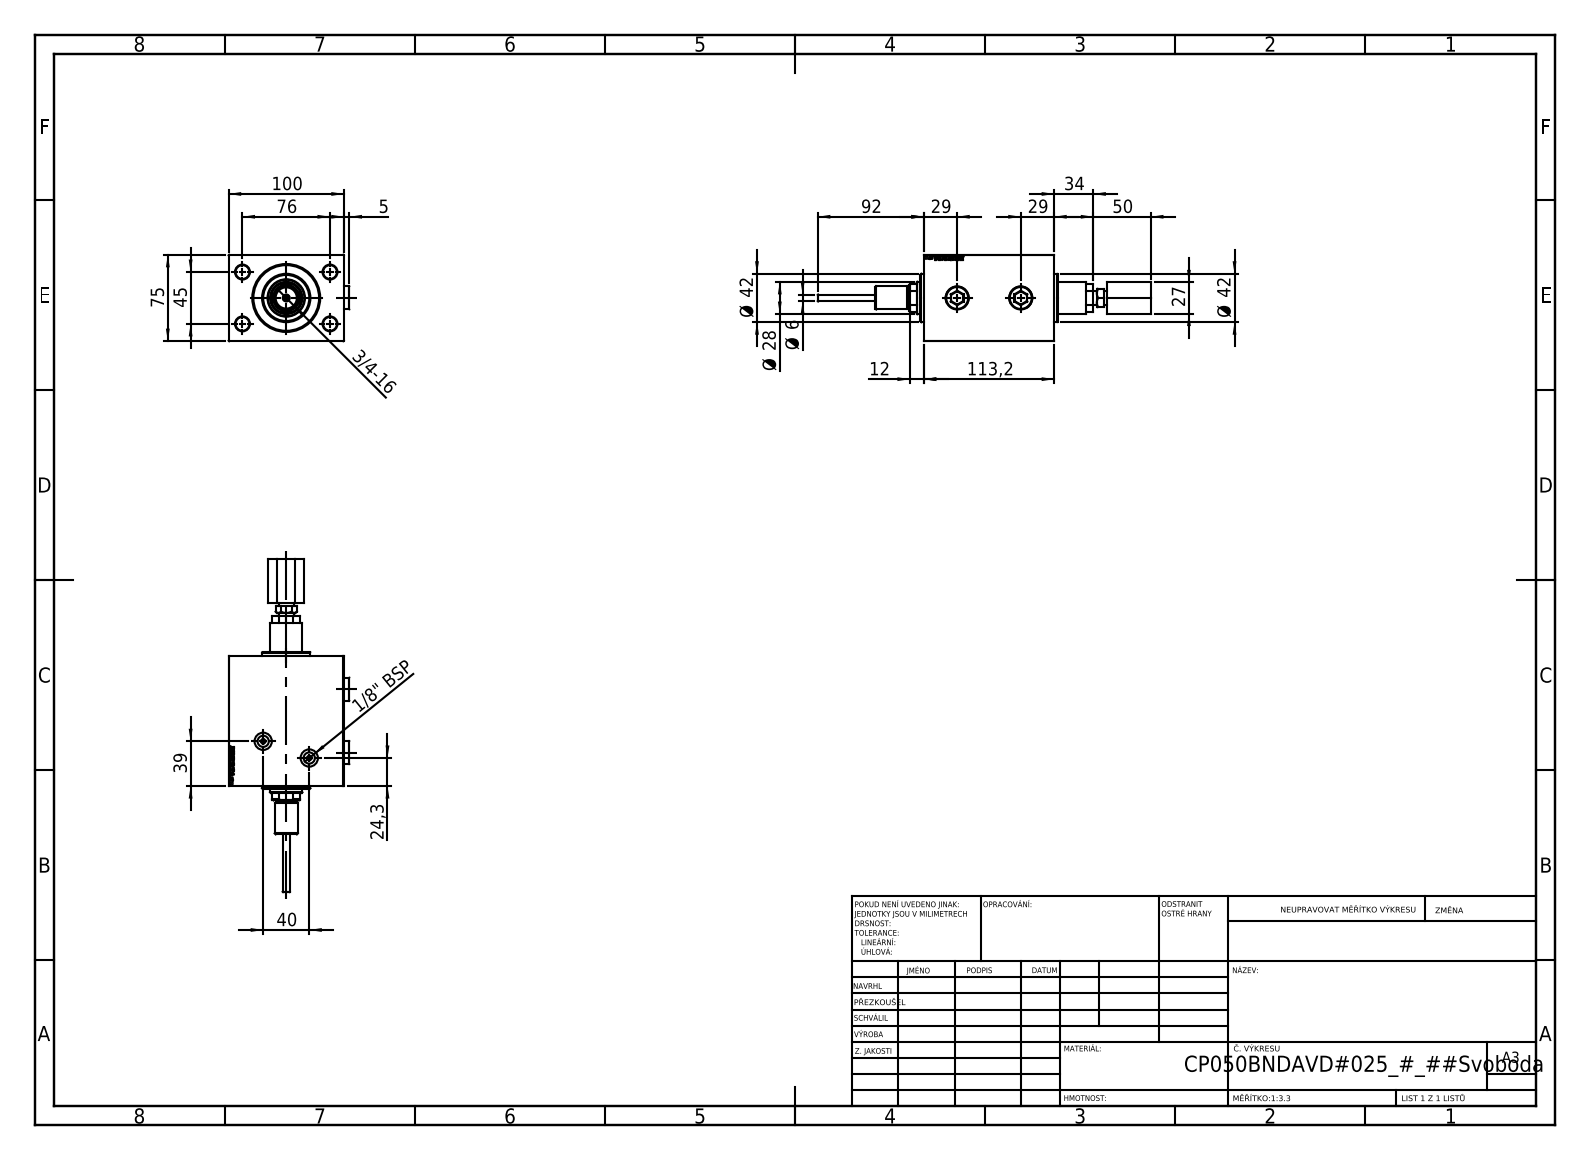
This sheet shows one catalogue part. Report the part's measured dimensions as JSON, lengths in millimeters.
{"part_name": "PLUG; V450DCP_B_RodCooling_ACCESSORIES; V450DCP_B_VCP; V450CP_MALE_METRIC (+2 more)", "step_written_by": "SolidWorks 2019 (CONFIG_CONTROL_DESIGN)", "units": "millimeters", "bodies": {"solids": 7, "faces": 1040, "planar": 472, "cylindrical": 114, "other": 454}, "overall_size": [289.2, 104.9, 75], "volume_mm3": 847920, "surface_area_mm2": 135990, "round_holes": [[12, 4], [5, 3], [13.16, 3], [20, 3], [4, 2], [9.73, 2], [15, 2], [3, 1], [6, 1], [18.5, 1], [28, 1], [31.5, 1]], "round_bosses_or_shafts": [[42, 1], [20, 1], [18, 1], [12.78, 1]], "partial_cylinders_radius": [[13.5, 1]], "face_to_face_distances": [75, 100, 113.2, 14, 99.2, 13, 43, 1, 27, 112.2], "hole_center_spacings": [44.16, 45, 76, 88.32, 11, 42.55, 55.2, 66.2]}
